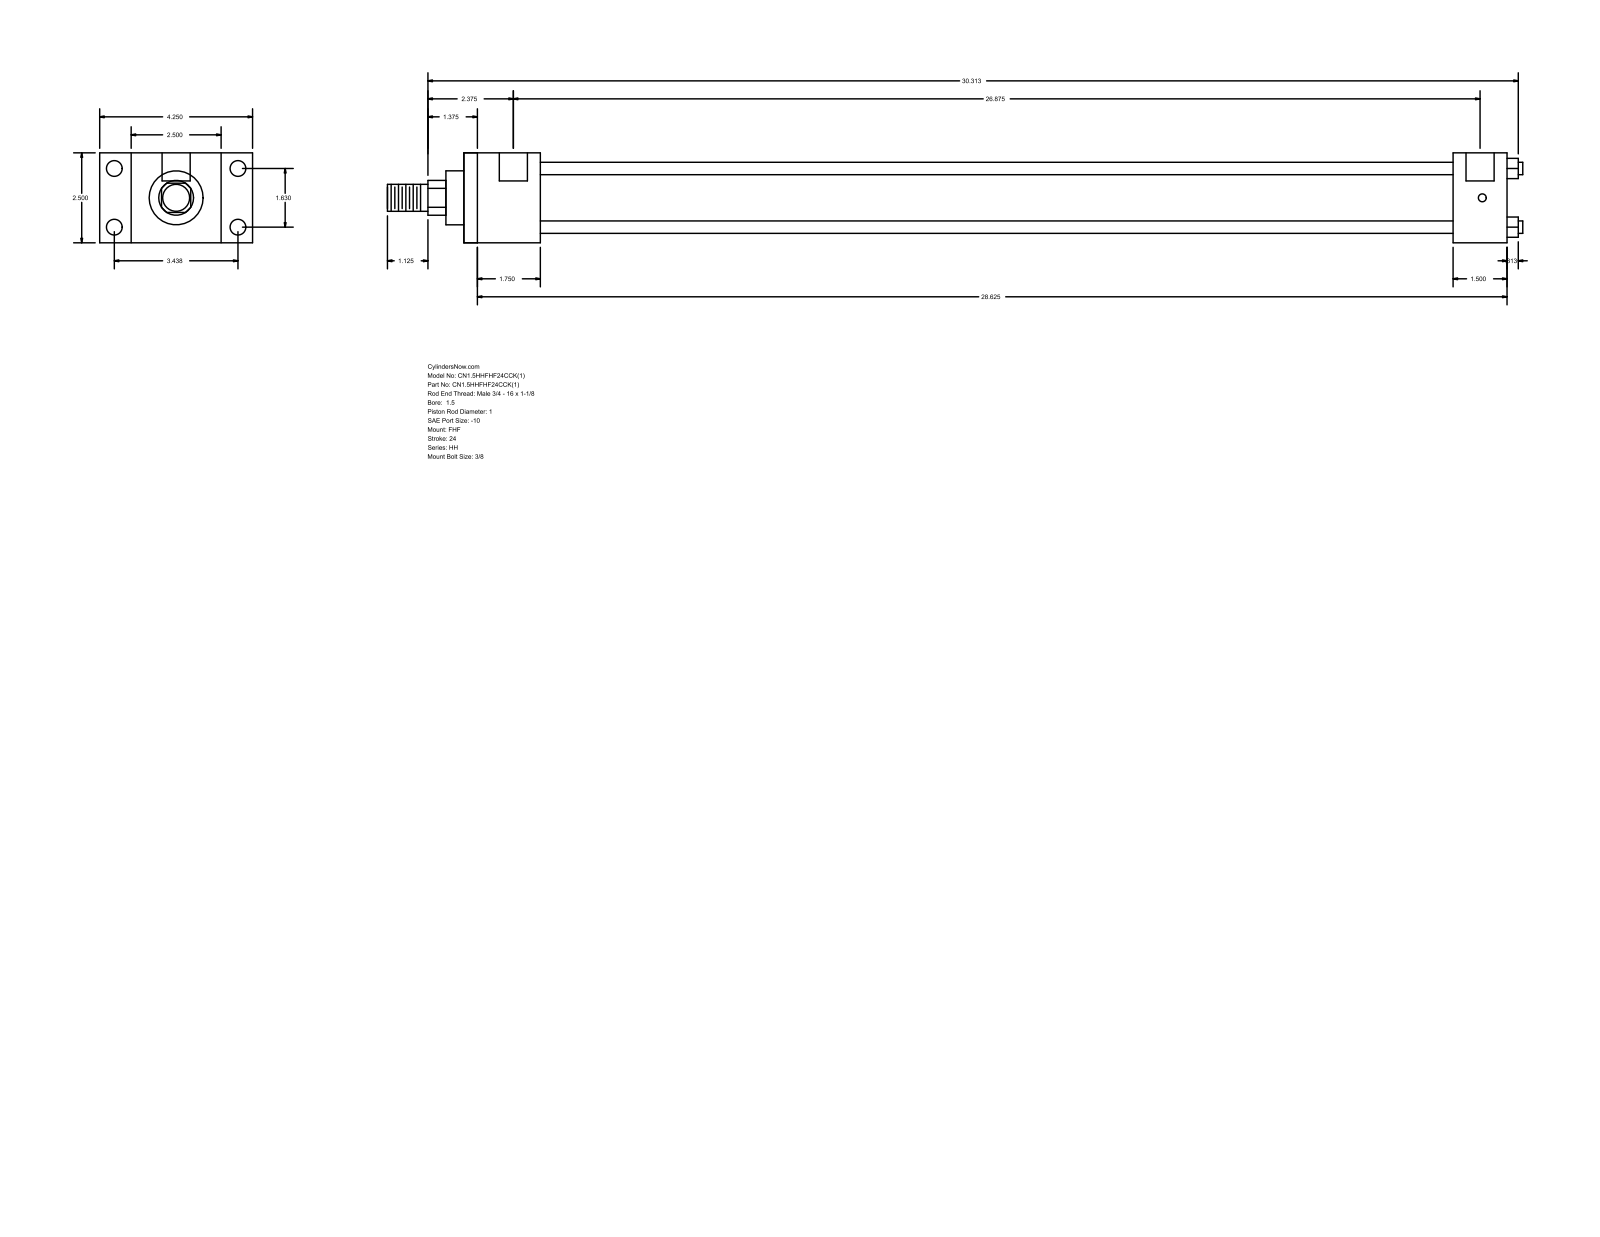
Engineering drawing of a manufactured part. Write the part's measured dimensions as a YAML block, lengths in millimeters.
part_name: "HH_FHF__0150_1"
step_written_by: "GSSL Pune (CONFIG_CONTROL_DESIGN)"
units: millimeters
bodies: {solids: 0, faces: 88, planar: 60, cylindrical: 28, other: 0}
overall_size: [801.69, 107.95, 63.5]
round_holes:
  - {diameter: 5.56, count: 4}
  - {diameter: 11.13, count: 4}
  - {diameter: 19.84, count: 2}
round_bosses_or_shafts:
  - {diameter: 8.76, count: 4}
  - {diameter: 44.45, count: 1}
  - {diameter: 38.1, count: 1}
  - {diameter: 25.4, count: 1}
  - {diameter: 19.05, count: 1}
partial_cylinders:
  - {radius: 12.29, count: 1}
face_to_face_distances: [63.5, 22.23, 85.73, 53.98, 107.96, 736.6, 682.62, 38.1, 698.5, 644.52]
hole_center_spacings: [1.59, 41.4, 87.32, 96.64, 684.21, 685.8, 682.62]
